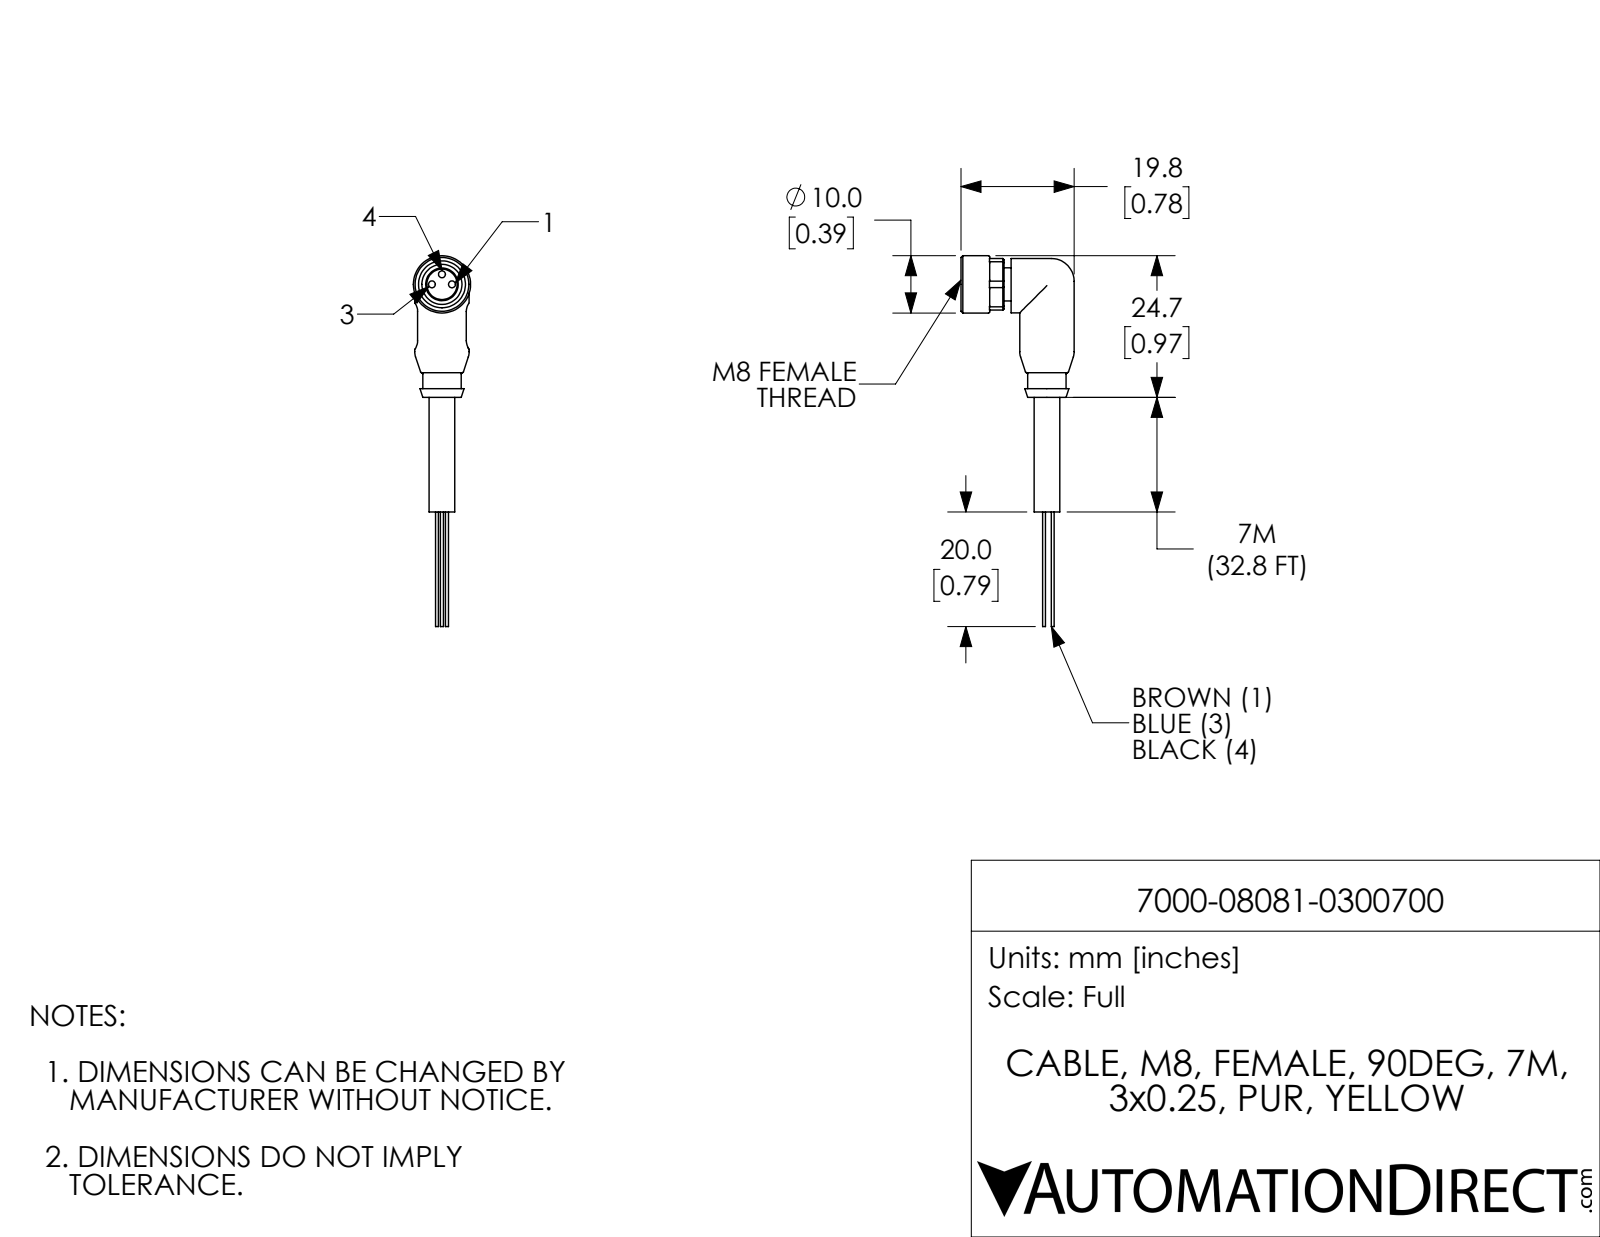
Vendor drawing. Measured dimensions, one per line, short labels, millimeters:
name: 7000-08081-0300700
written by: SolidWorks 2021 (CONFIG_CONTROL_DESIGN)
unit: mm
bodies: 1 solid, 107 faces (35 planar, 43 cylindrical, 29 other)
size: 64.7 × 19.8 × 10
volume: 2 410 mm³; area: 1 835 mm²
holes: 3× ⌀1.2, 1× ⌀7
bosses: 3× ⌀0.5, 2× ⌀9.5, 1× ⌀10, 1× ⌀6.7, 1× ⌀5.8, 1× ⌀5.7, 1× ⌀4.5
rounds: 4× R0.2, 4× R2.5, 1× R4.9
face distances: 1.2, 9, 1.5, 8.5, 0.7, 6.8, 8.1, 7.5, 8.7, 20
hole spacings: 1.8, 2.5, 3.5
